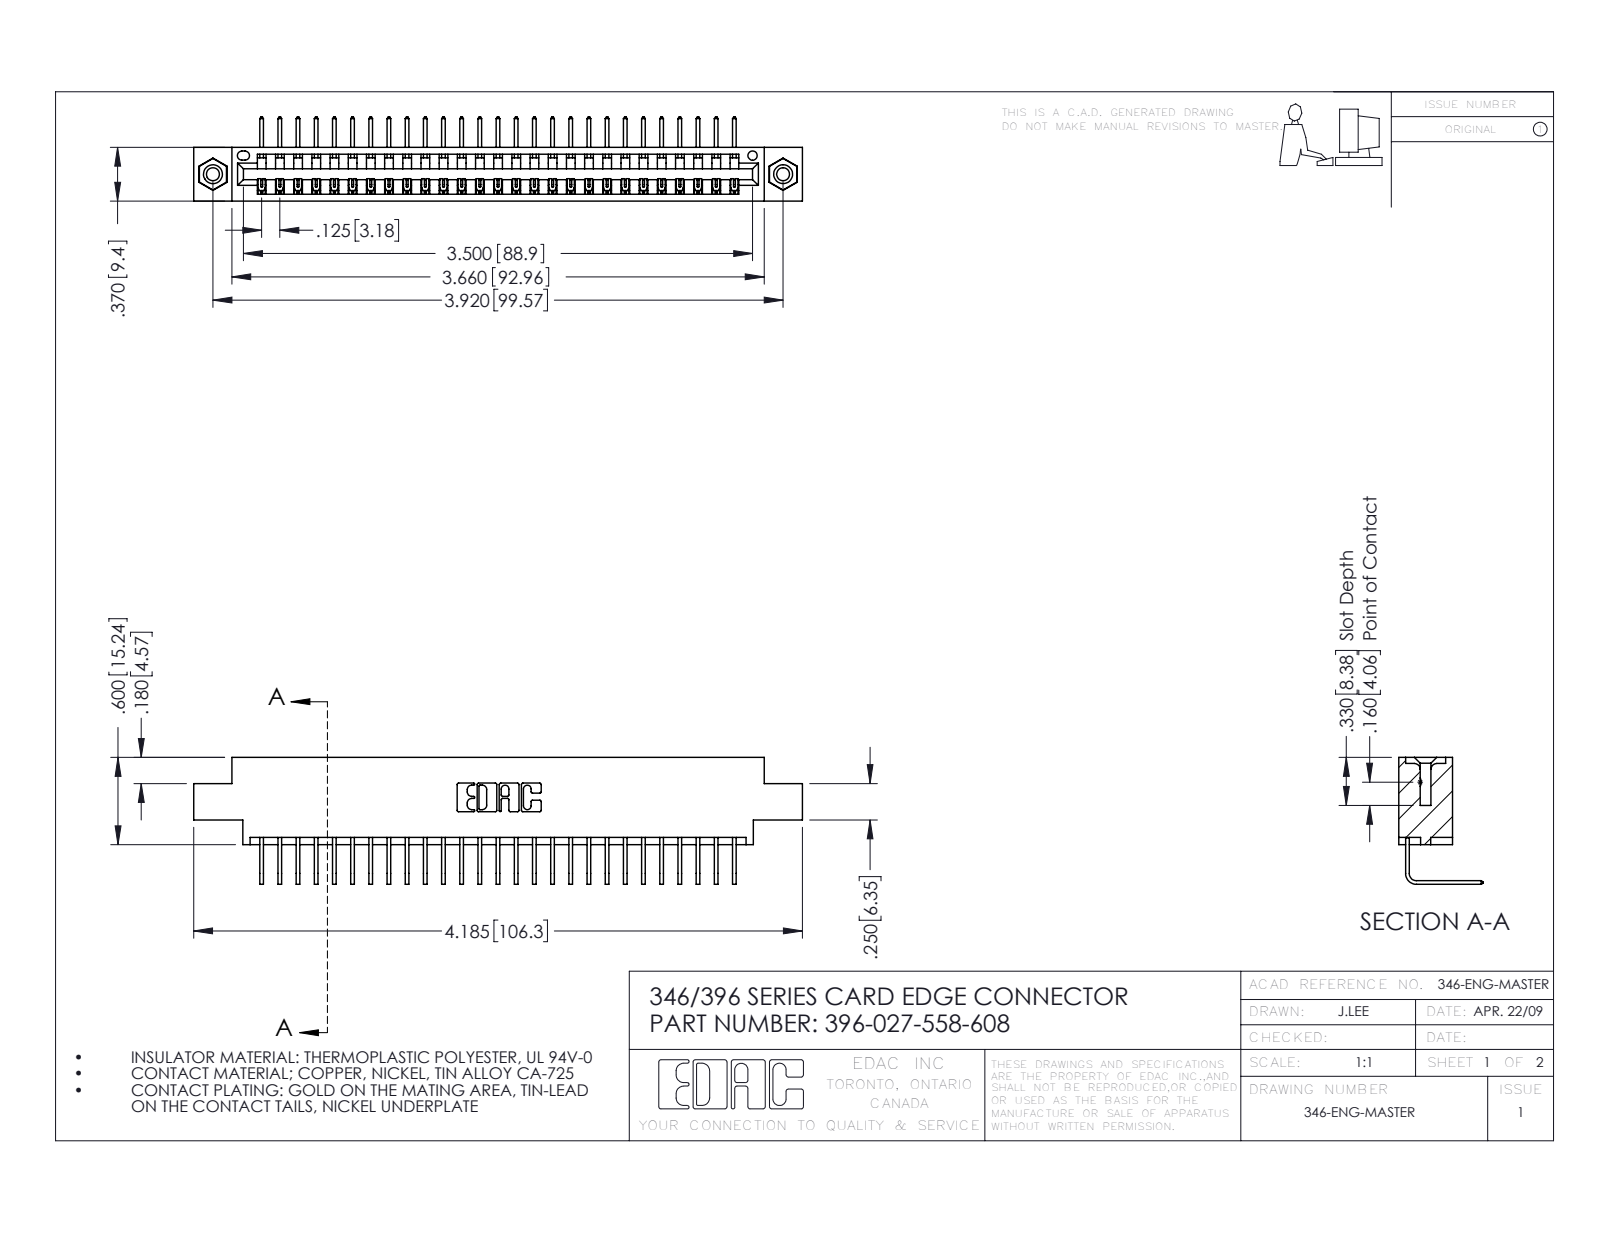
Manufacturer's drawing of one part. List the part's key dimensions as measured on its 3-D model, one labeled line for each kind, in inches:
Part name (STEP PRODUCT): 345-250-001_345-250-003-102; 346 Part_0.170 Offset - 0.156 Dia-TI; 396-027-558-608; 345-292-001_558 Tail - 2
STEP written by: SolidWorks 2016 (CONFIG_CONTROL_DESIGN)
Units: inches
Bodies: 30 solids, 1806 faces (1246 planar, 544 cylindrical, 16 other)
Overall size (bounding box): 4.185 × 0.873 × 0.58
Volume: 0.61 in³ · Surface area: 20.24 in²
Round holes (diameter × count): ⌀0.089 ×2, ⌀0.125 ×2, ⌀0.156 ×2, ⌀0.064 ×1
Round bosses / shafts (diameter × count): ⌀0.155 ×2
Partial cylindrical surfaces — rounded edges, fillets, slot ends (radius × count): R0.006 ×54, R0.01 ×22, R0.007 ×6, R0.031 ×6, R0.026 ×3, R0.031 ×2, R0.04 ×2, R0.014 ×1
Main face-to-face distances: 0.322, 0.048, 0.37, 0.25, 0.298, 0.025, 0.072, 0.222, 0.148, 0.1
Hole centre spacings: 0.246, 3.712, 3.92
